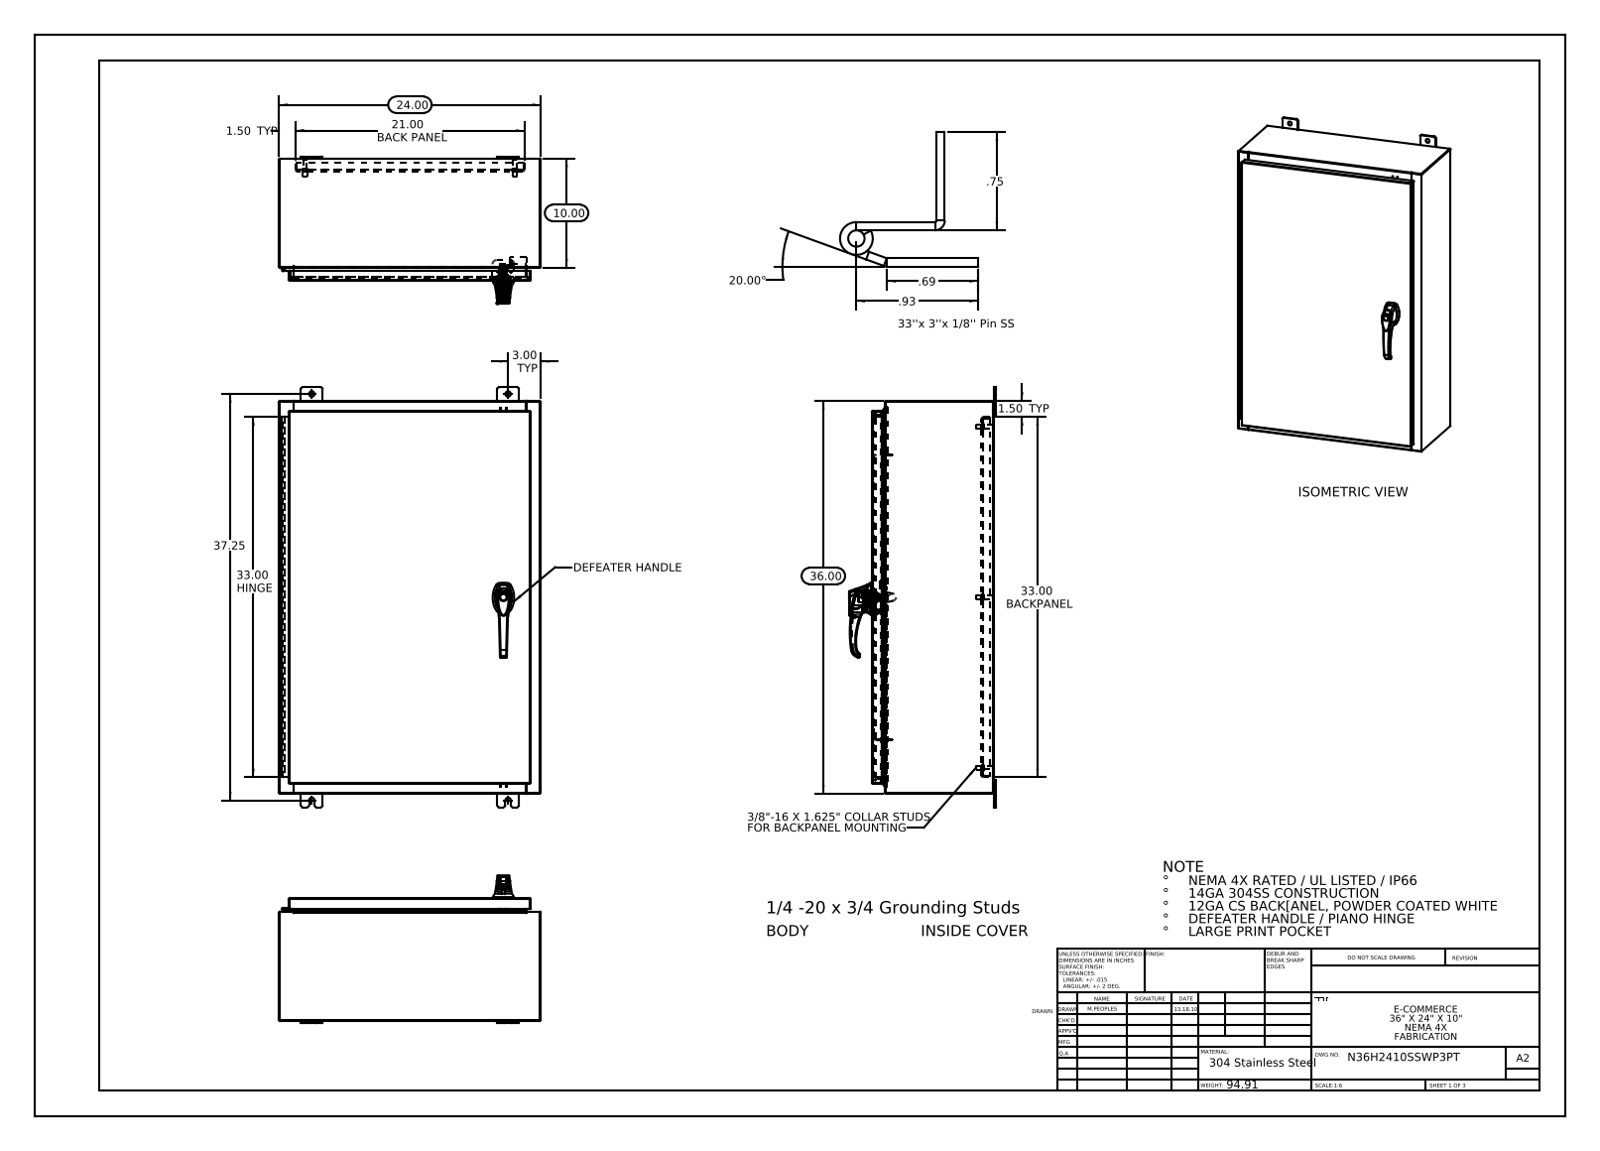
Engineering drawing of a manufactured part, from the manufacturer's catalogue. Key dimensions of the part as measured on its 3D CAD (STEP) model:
Part name (STEP PRODUCT): 033060_032151; N36H2410SSWP3PT Cover; N36H2410SSWP3PT Hinge Cover Side; N36H2410SSWP3PT Defeater Handle - 3 - 2500-51 ZN (+8 more)
STEP written by: SolidWorks 2013 (CONFIG_CONTROL_DESIGN)
Units: inches
Bodies: 33 solids, 2770 faces (1035 planar, 1061 cylindrical, 674 other)
Overall size (bounding box): 38.5 × 24 × 13.495
Volume: 336.3 in³ · Surface area: 8 336 in²
Round holes (diameter × count): ⌀0.5 ×10, ⌀0.25 ×4, ⌀0.138 ×3, ⌀0.161 ×3, ⌀0.079 ×2, ⌀0.203 ×2, ⌀0.313 ×2, ⌀0.437 ×2, ⌀0.125 ×1, ⌀0.125 ×1, ⌀0.197 ×1, ⌀0.276 ×1
Round bosses / shafts (diameter × count): ⌀0.625 ×6, ⌀0.375 ×6, ⌀0.33 ×6, ⌀1.181 ×1, ⌀0.748 ×1, ⌀0.68 ×1, ⌀0.661 ×1, ⌀0.639 ×1
Partial cylindrical surfaces — rounded edges, fillets, slot ends (radius × count): R0.118 ×37, R0.006 ×33, R0.013 ×24, R0.19 ×24, R0.088 ×18, R0.039 ×15, R0.028 ×12, R0.008 ×6
Main face-to-face distances: 0.075, 11.126, 0.104, 11.051, 11.201, 23.925, 1, 1.075, 10.051, 10.126
Hole centre spacings: 11.363, 13.669, 15.625, 24.793, 19.25, 0.295, 0.625, 0.841
